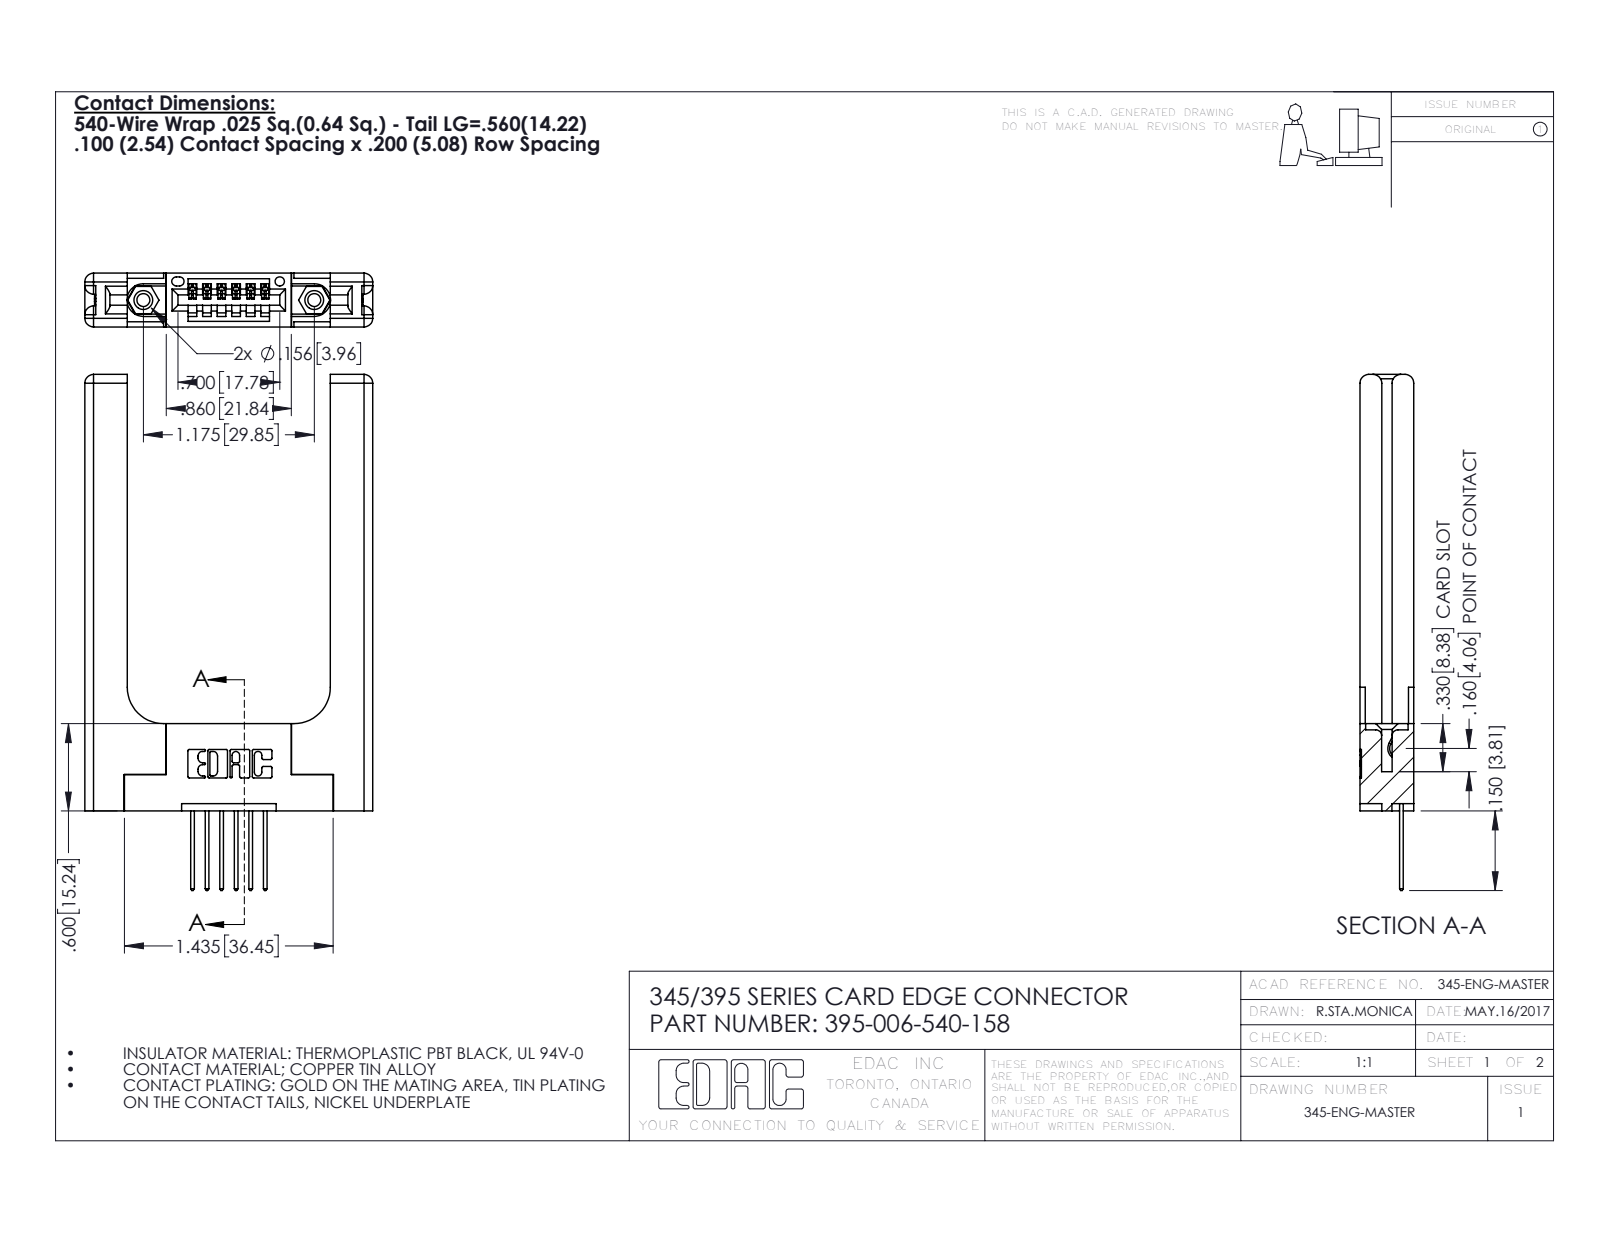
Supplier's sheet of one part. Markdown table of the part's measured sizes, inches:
| quantity | value |
| --- | --- |
| part name | 345-250-001_345-250-001-102; 345-220-058_345-220-058; 345 Part_Flush Mounting Lugs - 0.156 Dia-TH; 345-292-001_345-293-140 (+1 more) |
| STEP written by | SolidWorks 2016 (CONFIG_CONTROL_DESIGN) |
| units | inches |
| bodies | 11 solids, 730 faces (468 planar, 202 cylindrical, 60 other) |
| overall size | 3.547 × 1.979 × 0.37 |
| volume | 0.793 in³ |
| surface area | 16.8 in² |
| round holes (diameter × count) | 0.089 × 2, 0.125 × 2, 0.156 × 2, 0.064 × 1 |
| round bosses / shafts (diameter × count) | 0.155 × 2 |
| partial cylindrical surfaces (radius × count) | 0.01 × 22, 0.06 × 16, 0.006 × 12, 0.01 × 12, 0.007 × 6, 0.031 × 6, 0.026 × 3, 0.03 × 2 |
| main face-to-face distances | 0.37, 0.15, 0.22, 0.072, 0.077, 0.148, 1.396, 0.298, 0.071, 0.2 |
| hole center spacings | 0.27, 0.946, 1.175 |
